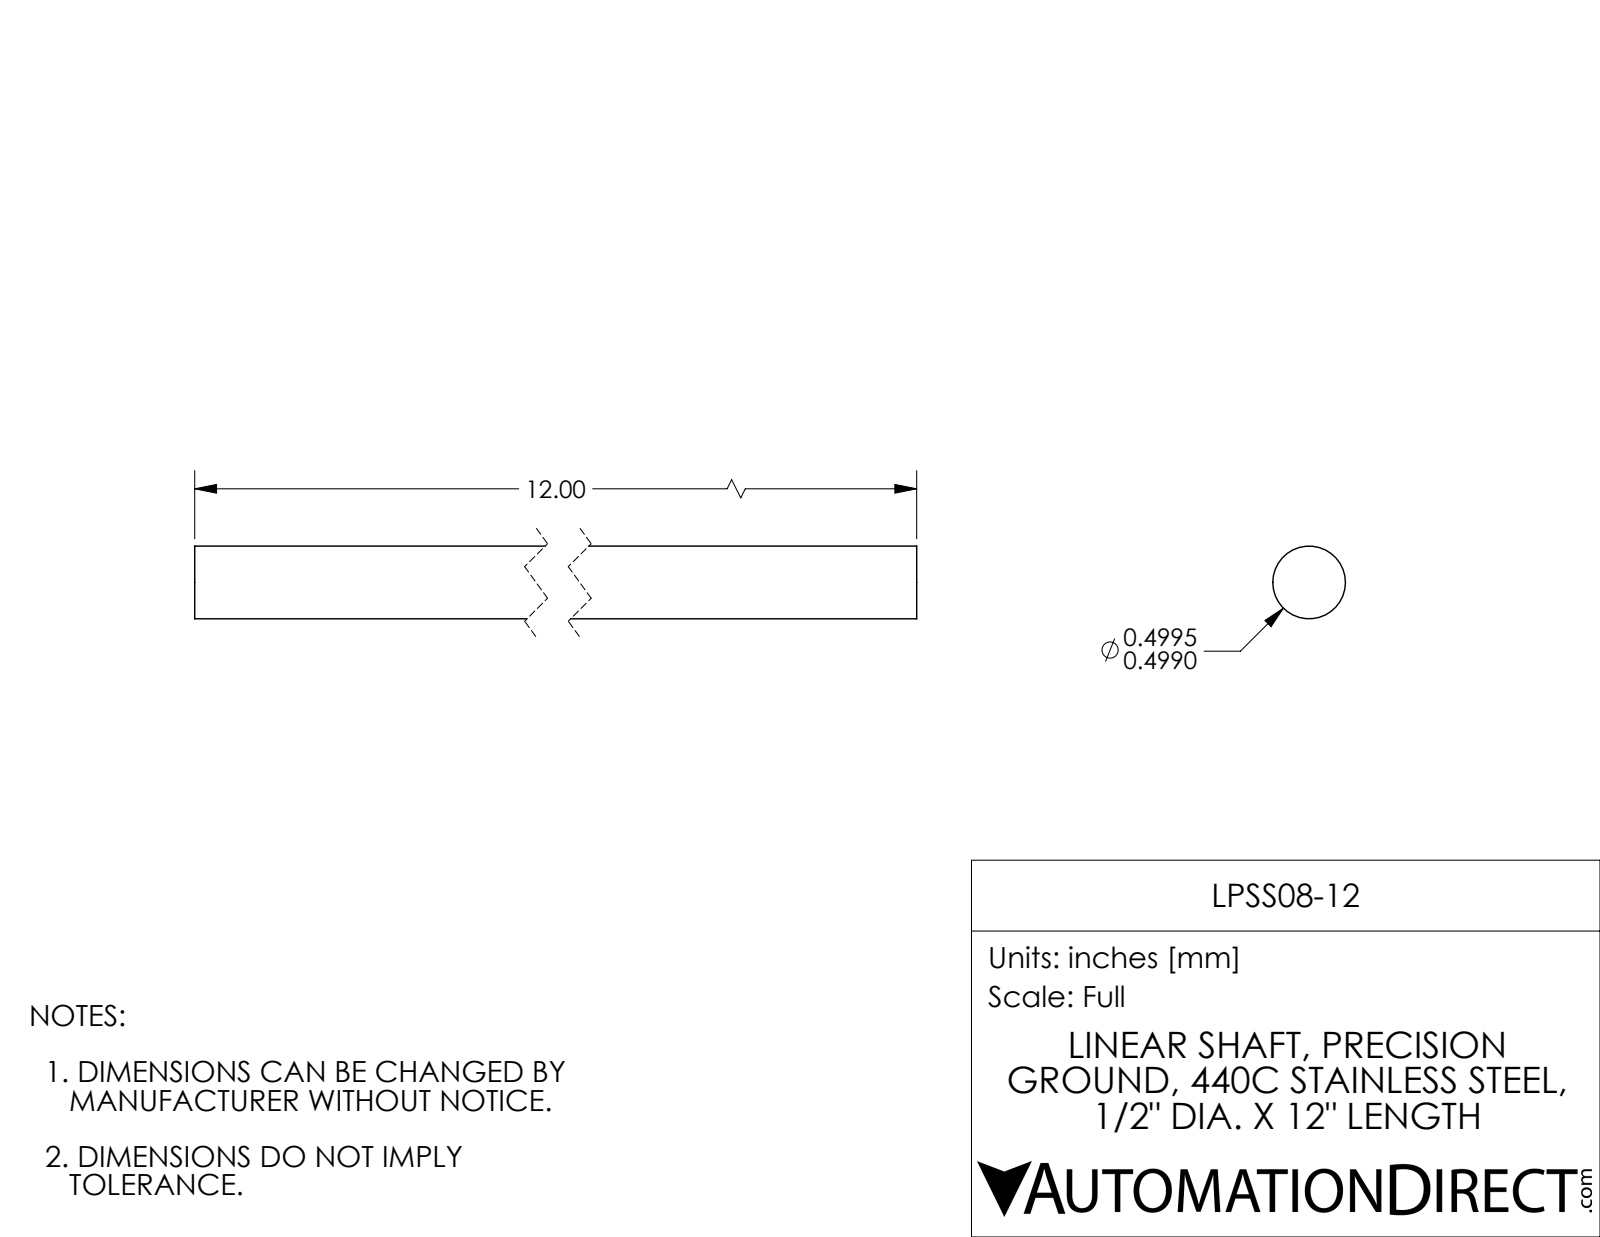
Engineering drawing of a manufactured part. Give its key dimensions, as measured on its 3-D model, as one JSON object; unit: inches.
{"part_name": "LPSS08-12", "step_written_by": "SolidWorks 2017 (AUTOMOTIVE_DESIGN)", "units": "inches", "bodies": {"solids": 1, "faces": 4, "planar": 2, "cylindrical": 2, "other": 0}, "overall_size": [12, 0.499, 0.499], "volume_in3": 2.351, "surface_area_in2": 19.22, "round_bosses_or_shafts": [[0.5, 1]], "face_to_face_distances": [12]}
